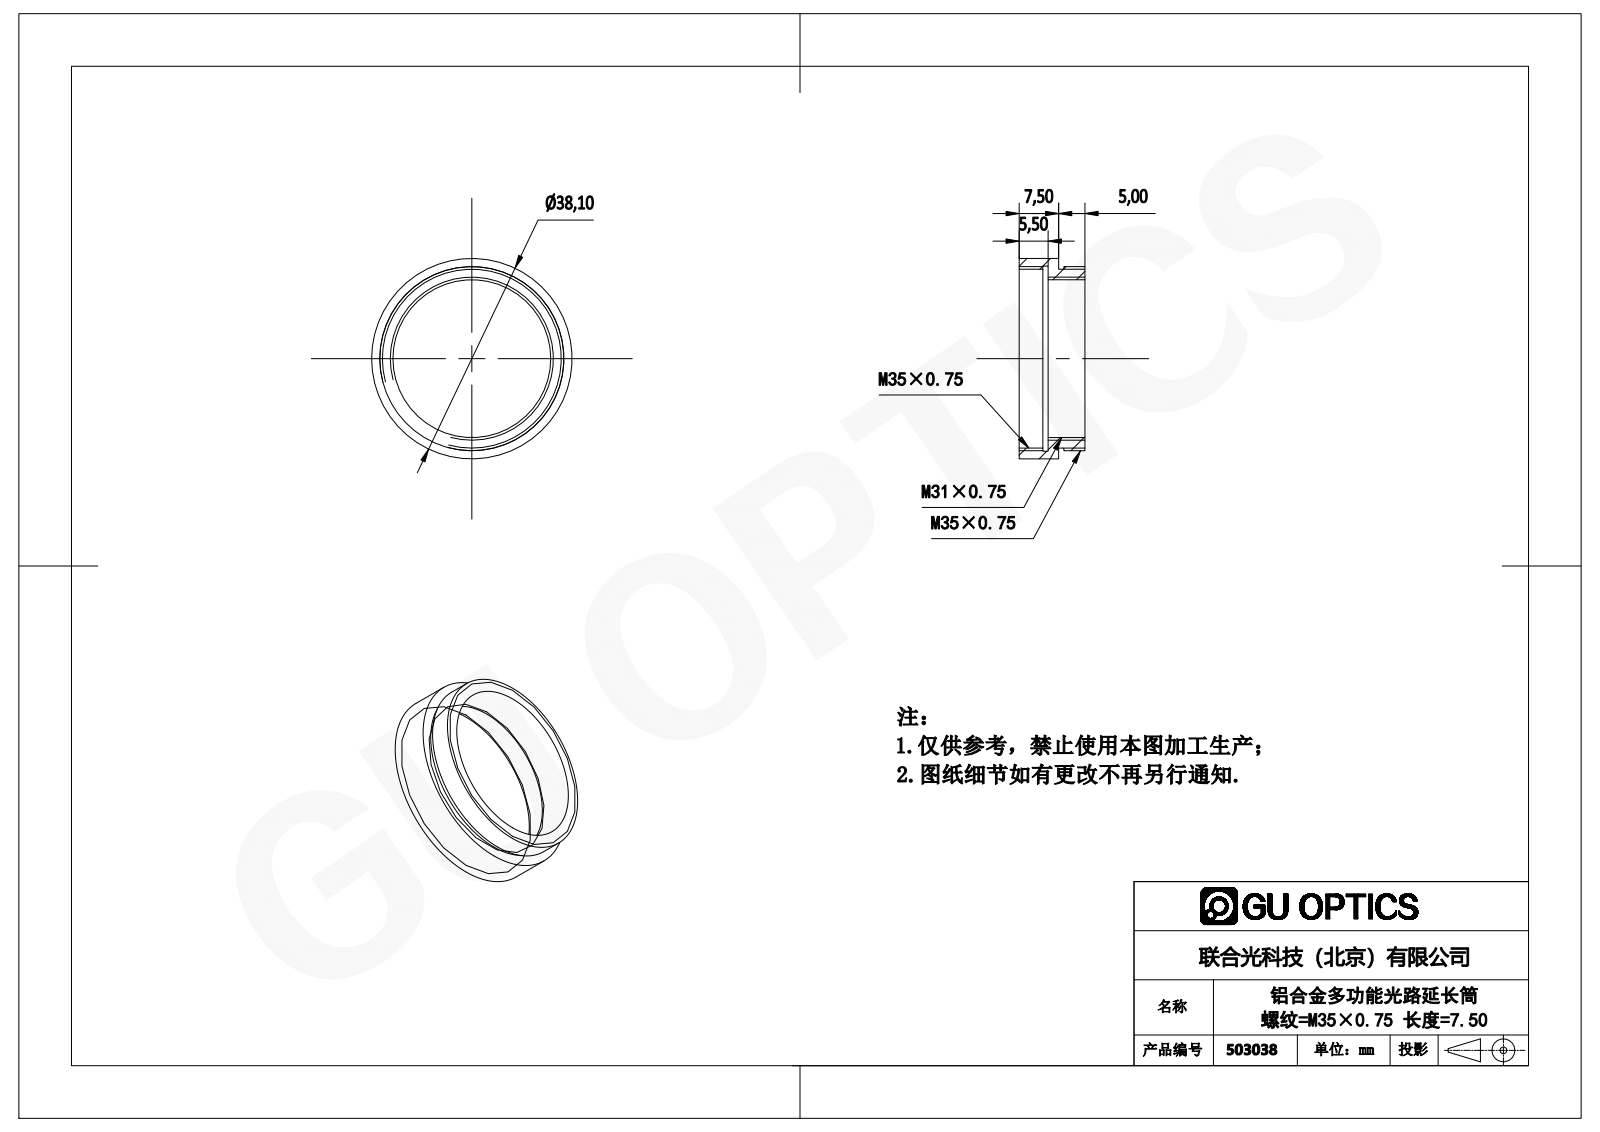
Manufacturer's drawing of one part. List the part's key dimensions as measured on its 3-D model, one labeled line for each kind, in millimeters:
Part name (STEP PRODUCT): 503038
STEP written by: SolidWorks 2016 (AUTOMOTIVE_DESIGN)
Units: millimetres
Bodies: 1 solid, 18 faces (6 planar, 12 cylindrical, 0 other)
Overall size (bounding box): 38.1 × 38.1 × 12.5
Volume: 3 300 mm³ · Surface area: 3 801 mm²
Round holes (diameter × count): ⌀30 ×1, ⌀34 ×1, ⌀35.2 ×1
Round bosses / shafts (diameter × count): ⌀38.1 ×1, ⌀35 ×1
Main face-to-face distances: 7, 2, 5, 5.5, 7.5, 12.5, 1, 3, 4, 4.5
